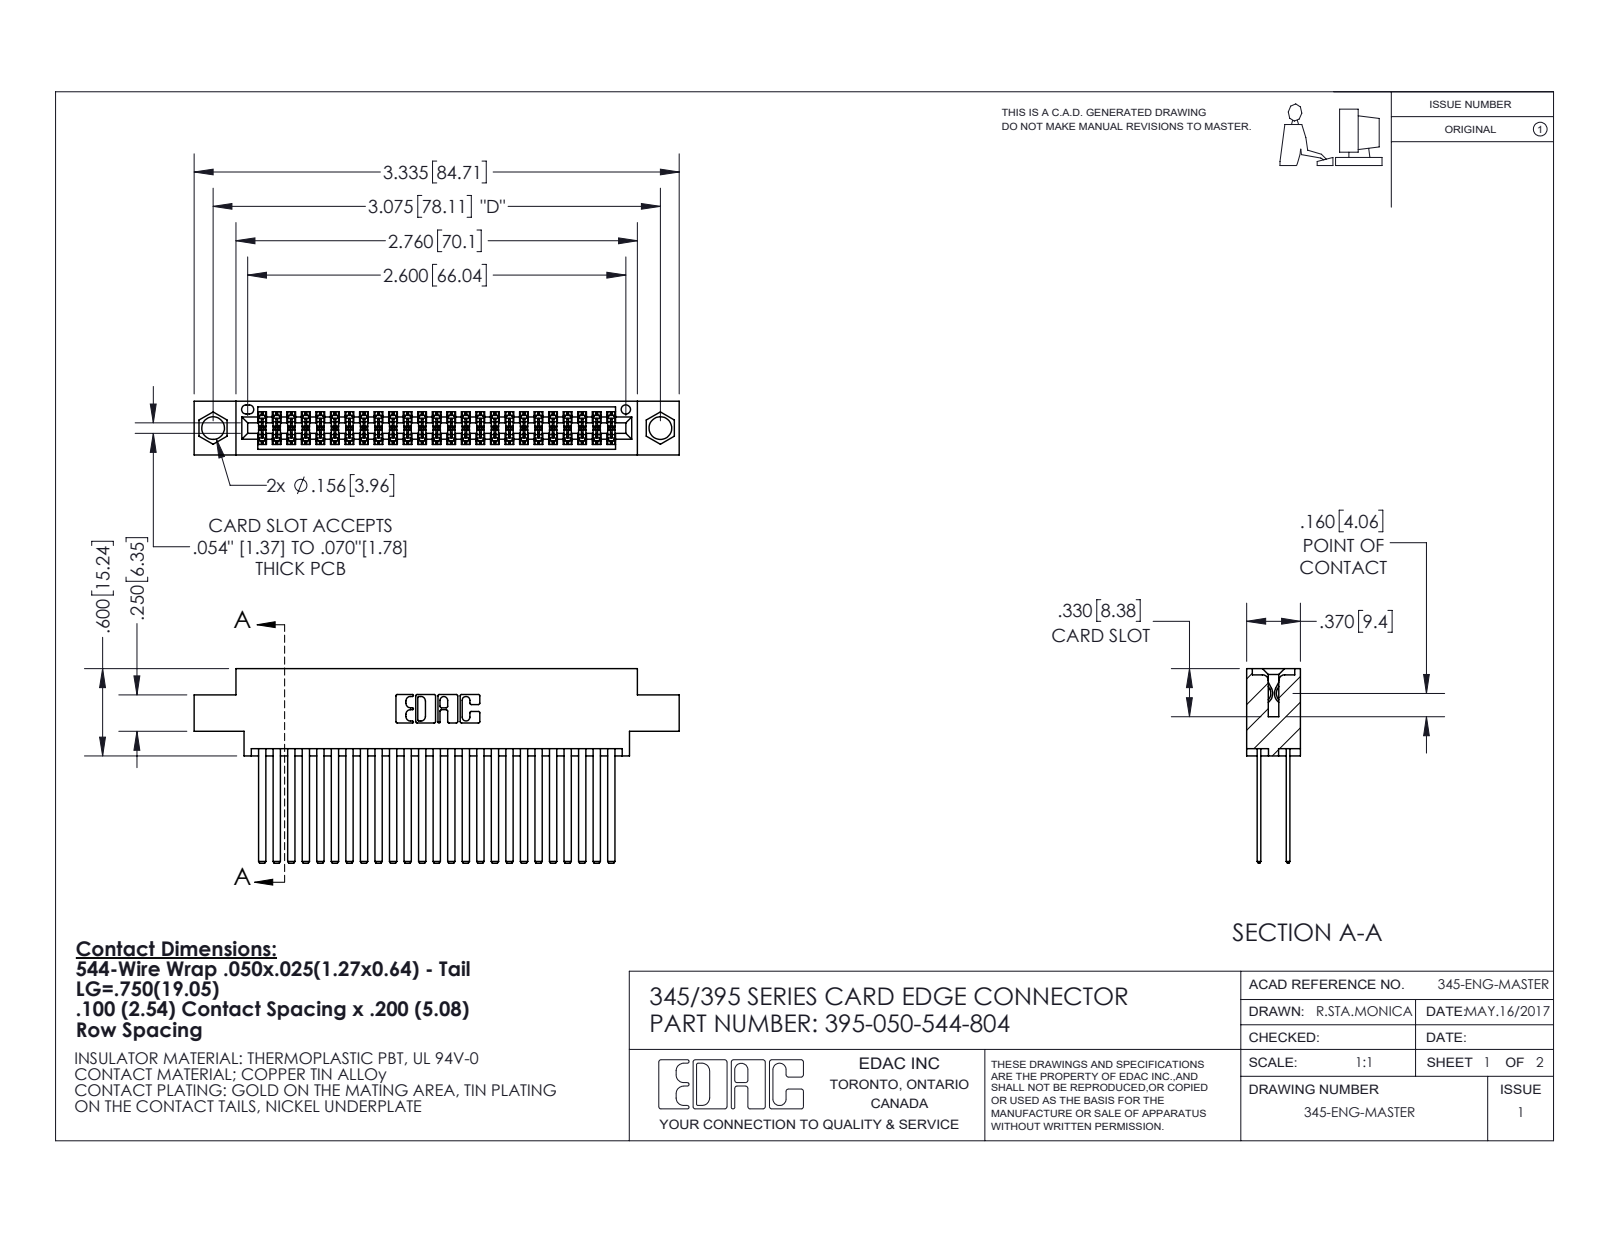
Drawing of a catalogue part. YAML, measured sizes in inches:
part_name: "395-050-544-804; 345 Part_0.170 Offset - 0.156 Dia-TI; 345-292-001_345-293-144"
step_written_by: "SolidWorks 2020 (CONFIG_CONTROL_DESIGN)"
units: inches
bodies: {solids: 51, faces: 2344, planar: 1548, cylindrical: 796, other: 0}
overall_size: [3.335, 1.337, 0.37]
volume: 0.522
surface_area: 22.26
round_holes:
  - {diameter: 0.156, count: 2}
  - {diameter: 0.064, count: 1}
partial_cylinders:
  - {radius: 0.006, count: 75}
  - {radius: 0.01, count: 22}
  - {radius: 0.007, count: 6}
  - {radius: 0.031, count: 6}
  - {radius: 0.026, count: 3}
  - {radius: 0.014, count: 2}
  - {radius: 0.019, count: 2}
  - {radius: 0.022, count: 2}
face_to_face_distances: [0.2, 0.072, 0.298, 0.025, 0.098, 0.272, 0.225, 0.175, 0.37, 0.15]
hole_center_spacings: [0.27, 2.84, 3.075]
